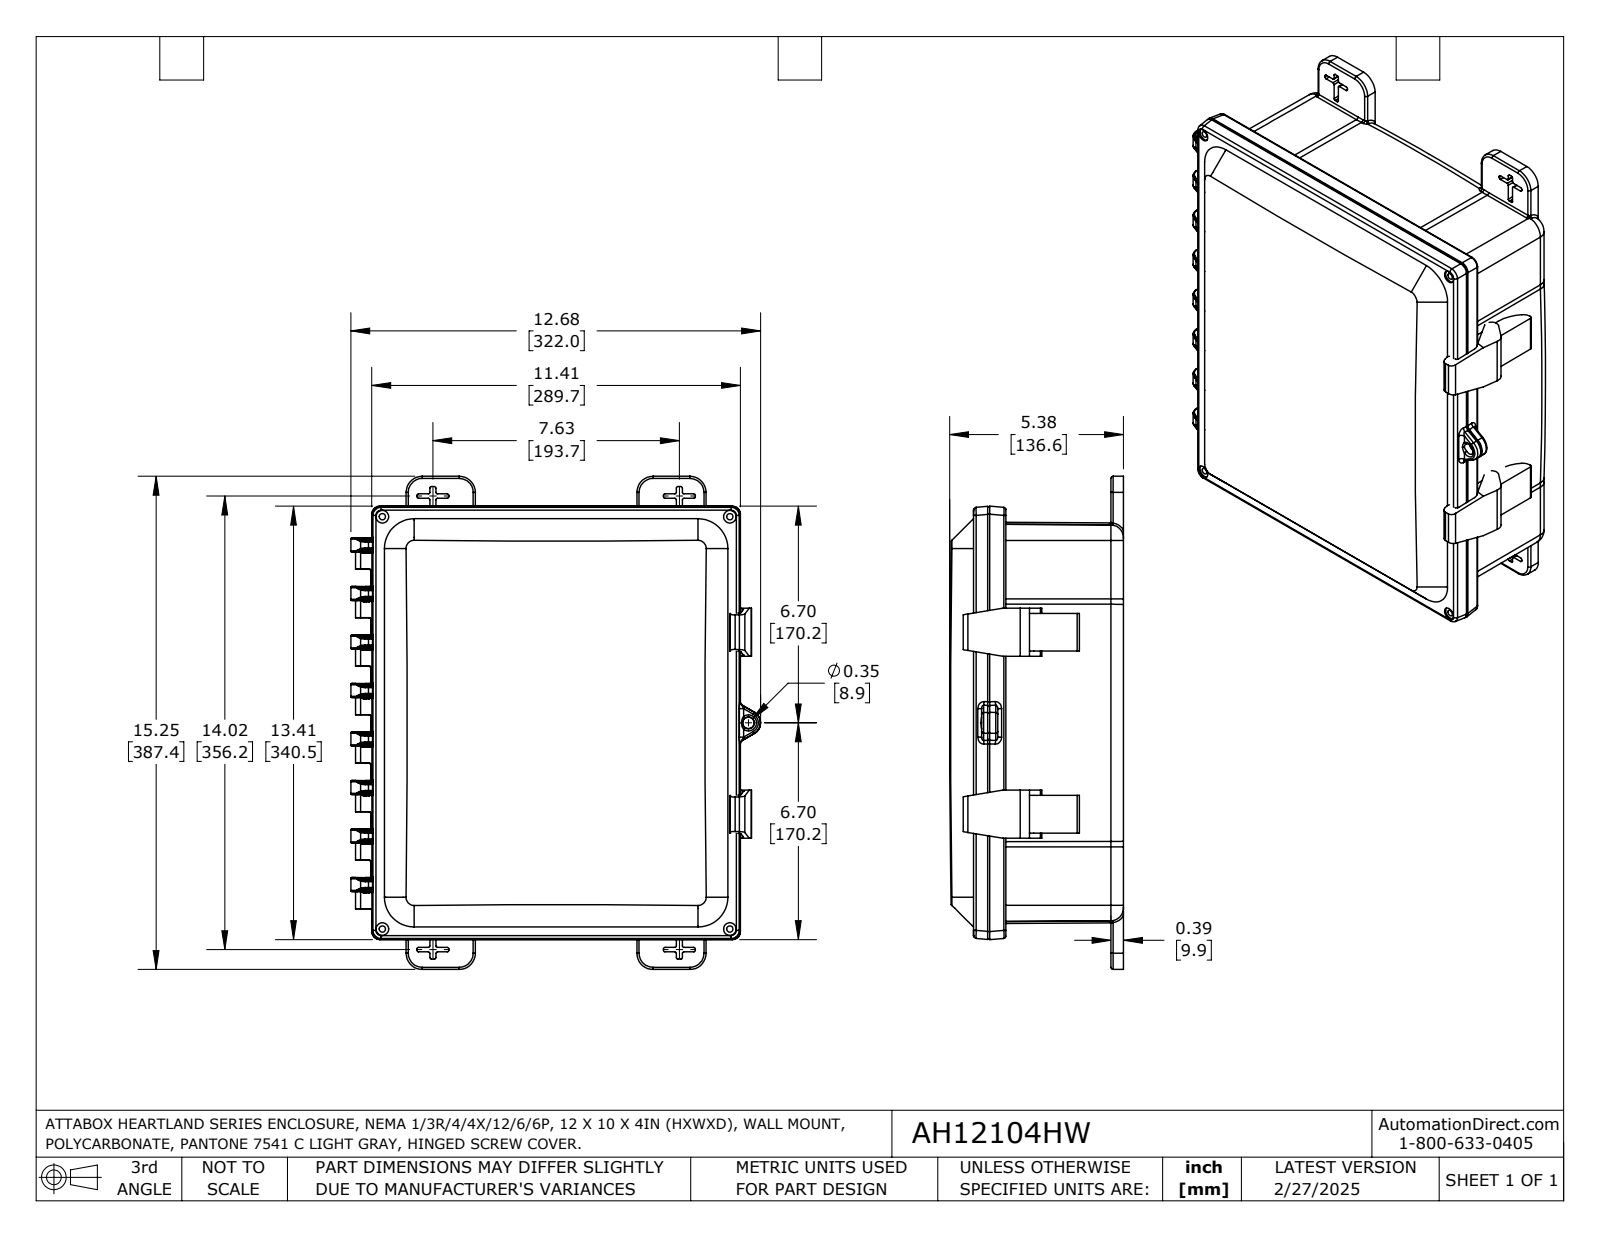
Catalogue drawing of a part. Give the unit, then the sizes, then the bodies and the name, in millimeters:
Units: millimetres
Overall size (bounding box): 387.4 × 322 × 136.6
Round holes (diameter × count): ⌀5 ×4, ⌀7.3 ×4, ⌀9.9 ×4, ⌀8.3 ×1, ⌀9.5 ×1, ⌀11.4 ×1
Round bosses / shafts (diameter × count): ⌀8 ×1
Partial cylindrical surfaces — rounded edges, fillets, slot ends (radius × count): R0.9 ×128, R1.7 ×94, R0.6 ×26, R0.3 ×25, R0.5 ×16, R12.7 ×12, R3.3 ×9, R6.4 ×8
Main face-to-face distances: 3.6, 101.6, 105.2, 3.6, 12.7, 4.7, 92.5, 88.9, 114.3, 25.4
Hole centre spacings: 44.9, 243.4, 293.8, 378.9, 138.2, 162.6, 209.6, 260.4
Volume: 1 708 000 mm³ · Surface area: 750 300 mm²
Bodies: 6 solids, 1856 faces (501 planar, 553 cylindrical, 802 other)
Part name (STEP PRODUCT): AH12104C
STEP written by: SolidWorks 2023 (AUTOMOTIVE_DESIGN)
